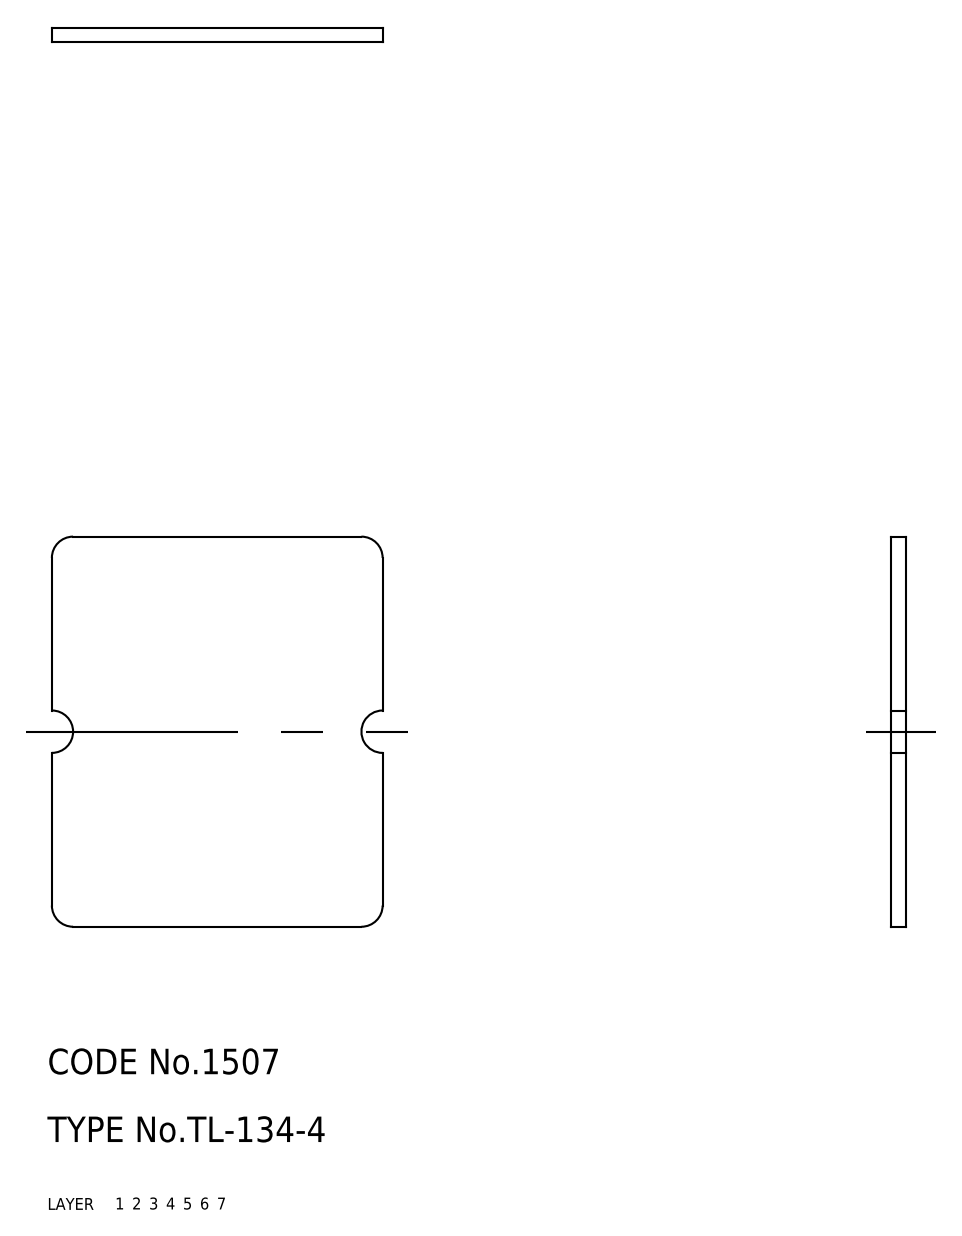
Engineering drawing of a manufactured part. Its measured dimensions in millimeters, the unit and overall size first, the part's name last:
Units: millimetres
Overall size (bounding box): 46 × 39 × 1.7
Volume: 3 007 mm³ · Surface area: 3 829 mm²
Bodies: 1 solid, 14 faces (0 planar, 0 cylindrical, 14 other)
Part name (STEP PRODUCT): spacer
STEP written by: CADfix (AUTOMOTIVE_DESIGN)
